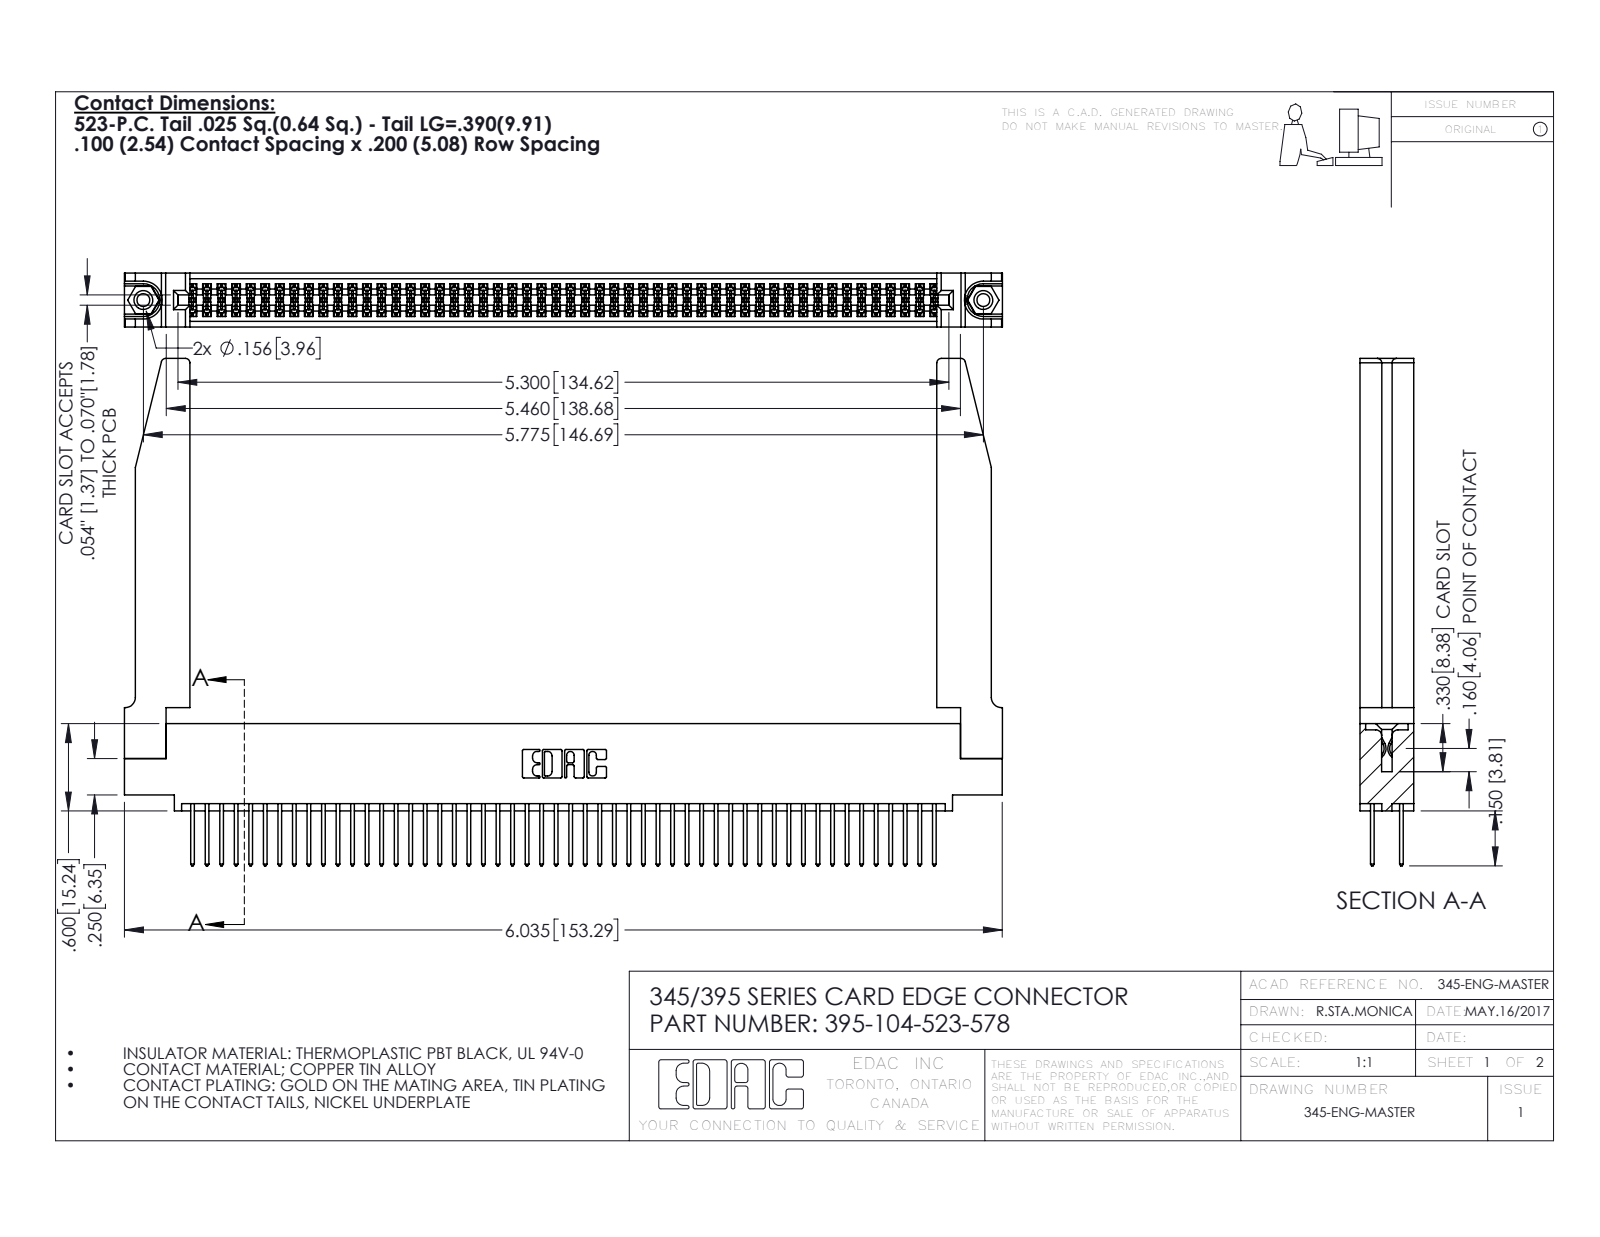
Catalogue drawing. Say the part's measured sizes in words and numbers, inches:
The part is named "345-220-078_345-220-078; 395-104-523-578; 345-250-001_345-250-001-102; 345 Part_0.110 Offset - 0.156 Dia-TH (+1 more)". Its 3-D file was written by "SolidWorks 2016 (CONFIG_CONTROL_DESIGN)". It is 109 solids with 5564 faces: 3658 planar, 1854 cylindrical and 52 other. Overall it measures 6.036 by 3.487 by 0.37 inches. Its volume is 1.397 cubic inches and its surface area 47.18 square inches. Round holes: 2 of diameter 0.089, 2 of diameter 0.125, 2 of diameter 0.156, 1 of diameter 0.064. Round bosses or shafts: 2 of diameter 0.155. Partial cylindrical surfaces (rounded edges, fillets, slot ends): 156 of radius 0.006, 104 of radius 0.01, 22 of radius 0.01, 8 of radius 0.03, 6 of radius 0.007, 6 of radius 0.031, 3 of radius 0.026, 2 of radius 0.014. The main face-to-face distances are 0.072, 0.298, 0.37, 0.098, 0.272, 0.025, 0.2, 0.225, 0.175, 0.15. The hole center spacings are 0.27, 5.539, 5.775.
